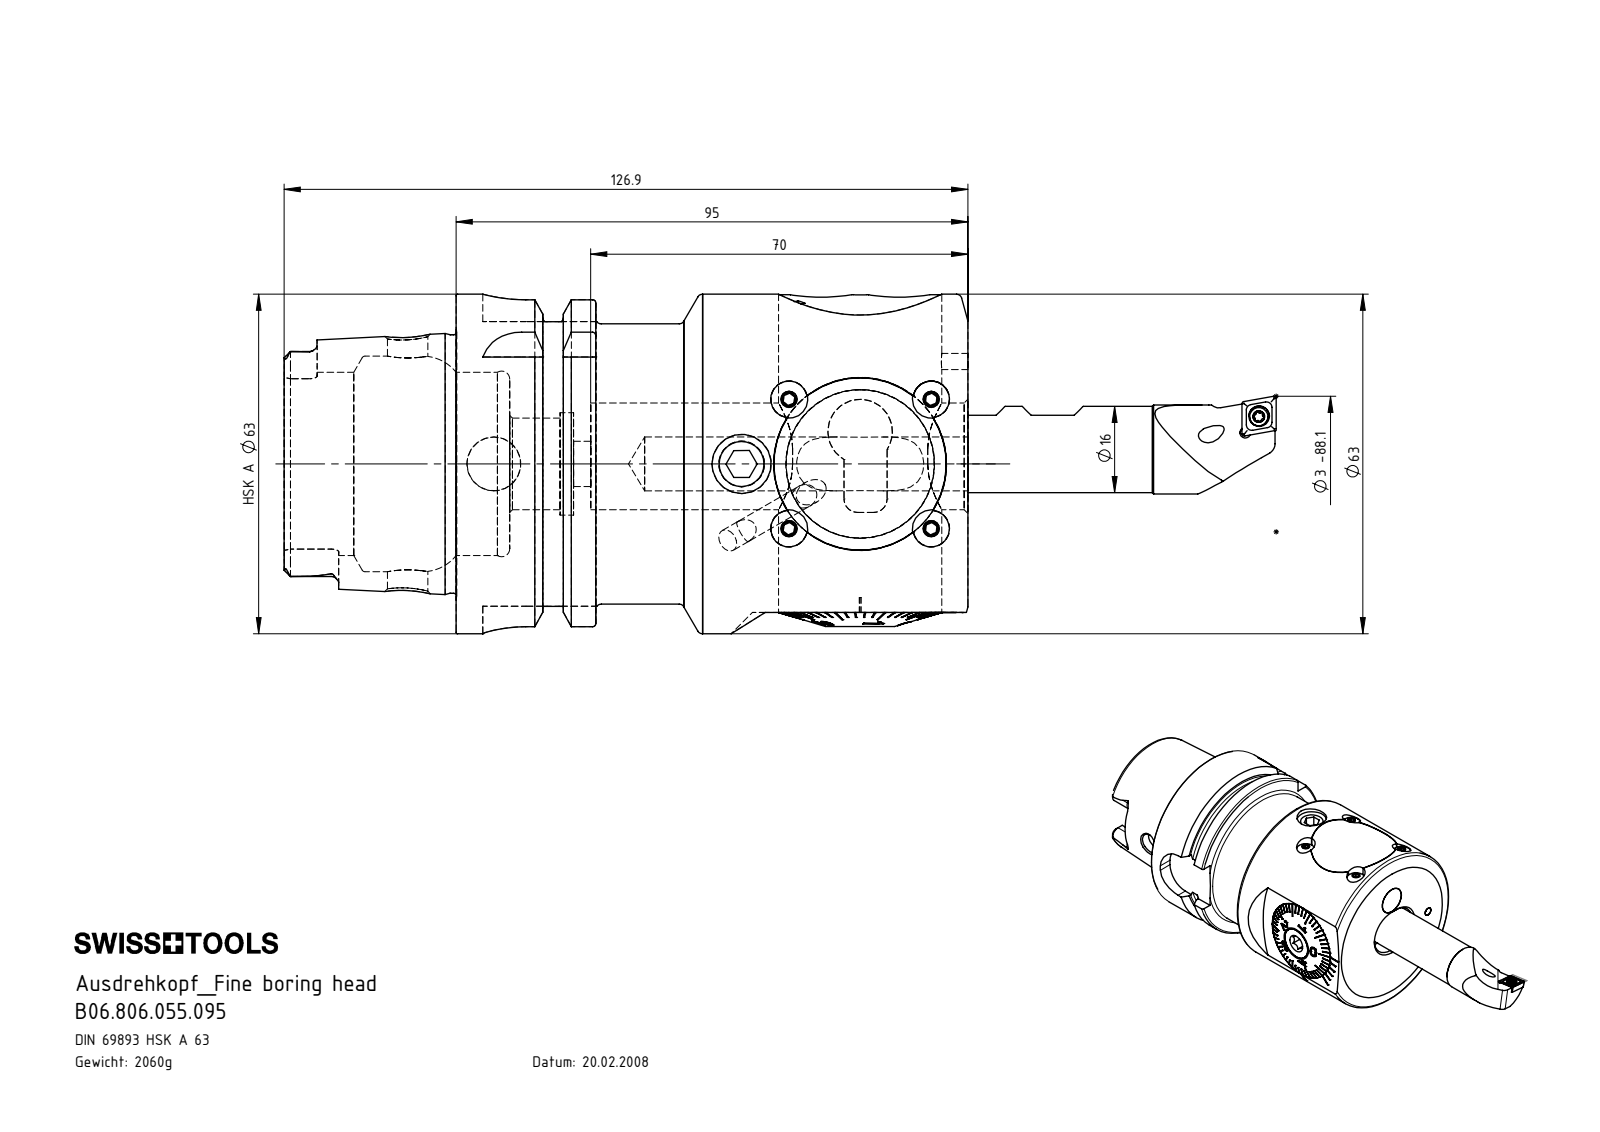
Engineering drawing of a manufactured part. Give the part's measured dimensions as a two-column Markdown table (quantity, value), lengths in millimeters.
| quantity | value |
| --- | --- |
| part name | B06.806.055.095; Glasmassstab; A63-ER5.001.006_A; Schutzhülle_eingebaut (+8 more) |
| STEP written by | SolidWorks 2017 (CONFIG_CONTROL_DESIGN) |
| units | millimeters |
| bodies | 43 solids, 1798 faces (761 planar, 394 cylindrical, 643 other) |
| overall size | 184.15 × 63 × 63 |
| volume | 265 306 mm³ |
| surface area | 90 719 mm² |
| round holes (diameter × count) | 1.6 × 6, 2.1 × 5, 2.5 × 4, 8.5 × 4, 3 × 2, 4.2 × 2, 2 × 1, 2.05 × 1, 2.8 × 1, 3.85 × 1, 6.8 × 1, 7.5 × 1 |
| round bosses / shafts (diameter × count) | 3 × 5, 10 × 4, 6.8 × 3, 27 × 2, 0.4 × 2, 63 × 1, 54.95 × 1, 52 × 1 |
| partial cylindrical surfaces (radius × count) | 1.5 × 28, 0.2 × 9, 0.21 × 6, 1.4 × 6, 0.36 × 5, 2.88 × 4, 3.5 × 4, 8 × 4 |
| main face-to-face distances | 6.3, 3, 1, 44.8, 95, 3.3, 7.3, 4.3, 43.8, 45.1 |
| hole center spacings | 11.63, 12.42, 17.84, 26.12, 7.25, 8.34, 10, 12.15 |
